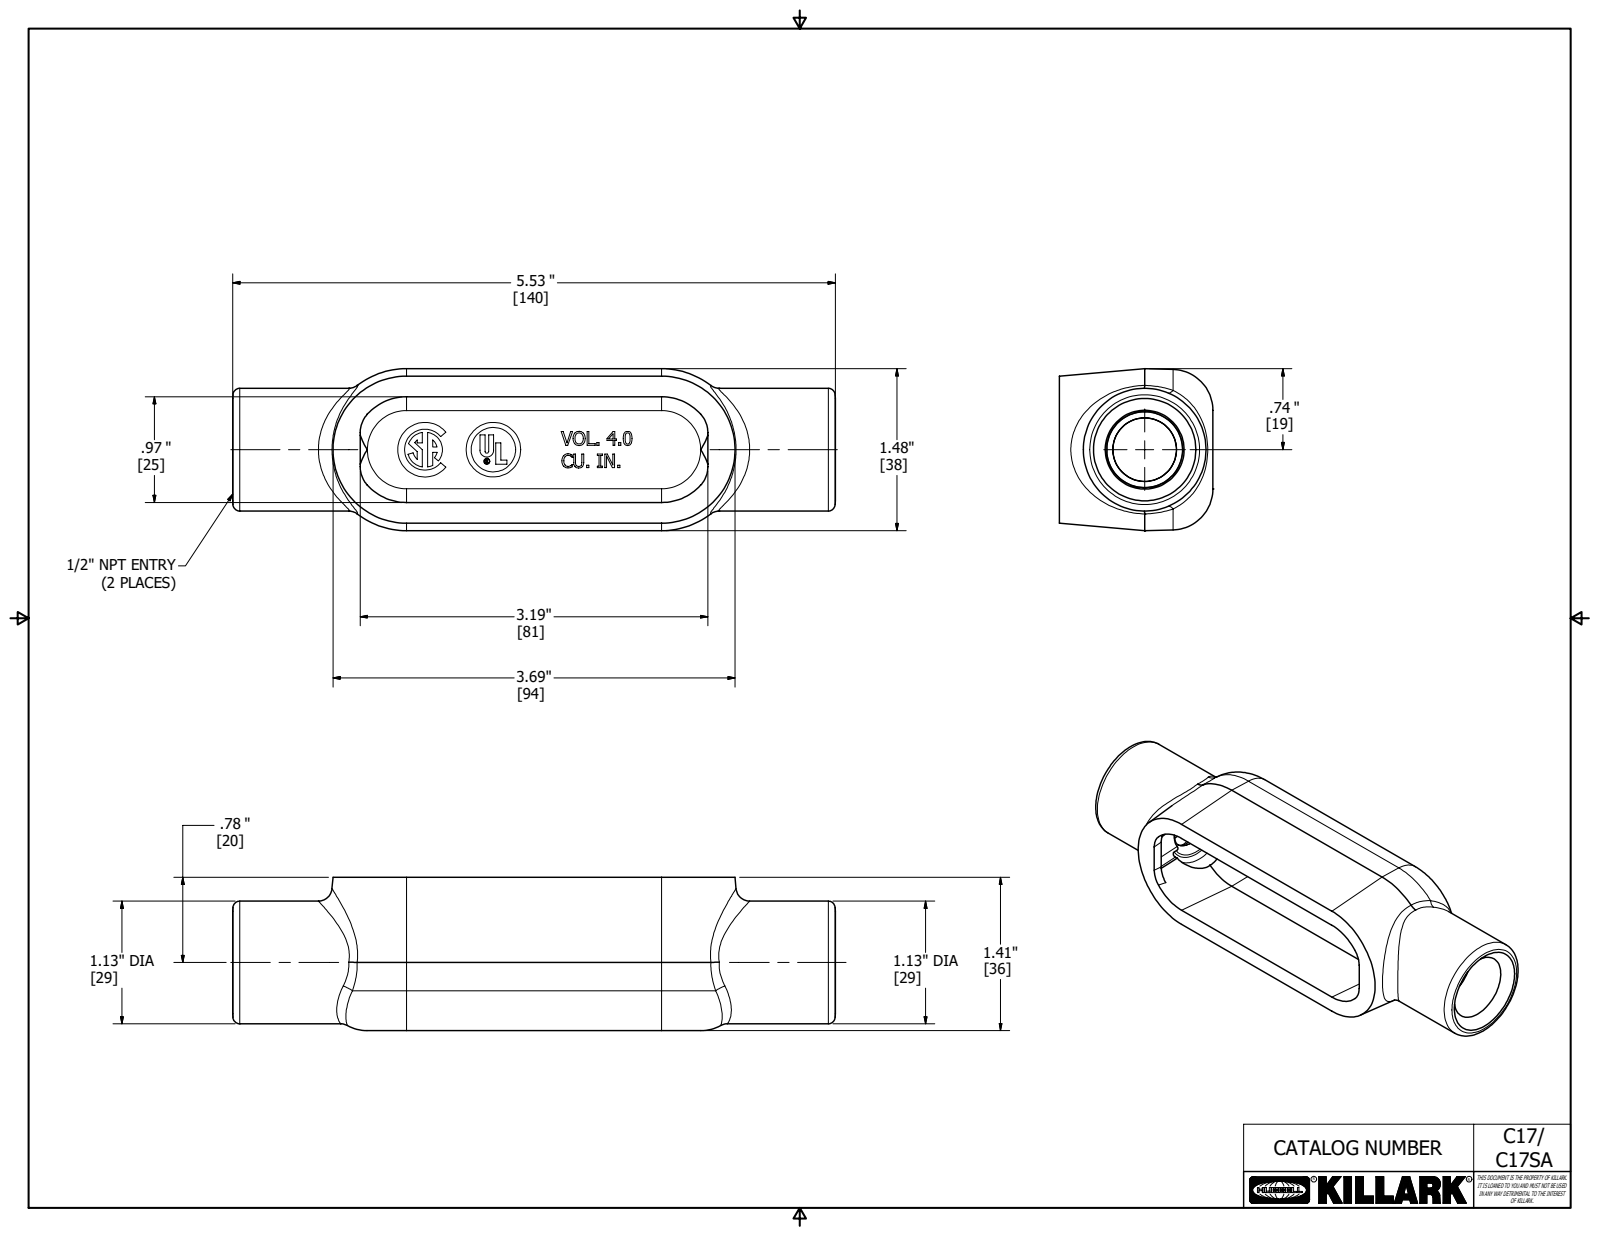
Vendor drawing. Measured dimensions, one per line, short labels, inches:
name: 17639-2
written by: Autodesk Inventor 2018 (AUTOMOTIVE_DESIGN)
unit: in
bodies: 1 solid, 433 faces (269 planar, 36 cylindrical, 128 other)
size: 5.525 × 1.484 × 1.406
volume: 3.601 in³; area: 42.21 in²
holes: 1× ⌀0.047, 1× ⌀0.407, 1× ⌀0.844, 1× ⌀0.875
bosses: 1× ⌀1.125, 1× ⌀0.5, 1× ⌀0.056
rounds: 4× R0.062, 4× R0.125, 3× R0.187, 2× R0.375, 1× R0.006, 1× R0.009, 1× R0.016, 1× R0.063
face distances: 0.189, 0.188, 1.406, 1.219, 0.189, 0.031, 0.156, 1.375, 0.031, 0.187
hole spacings: 0.122
